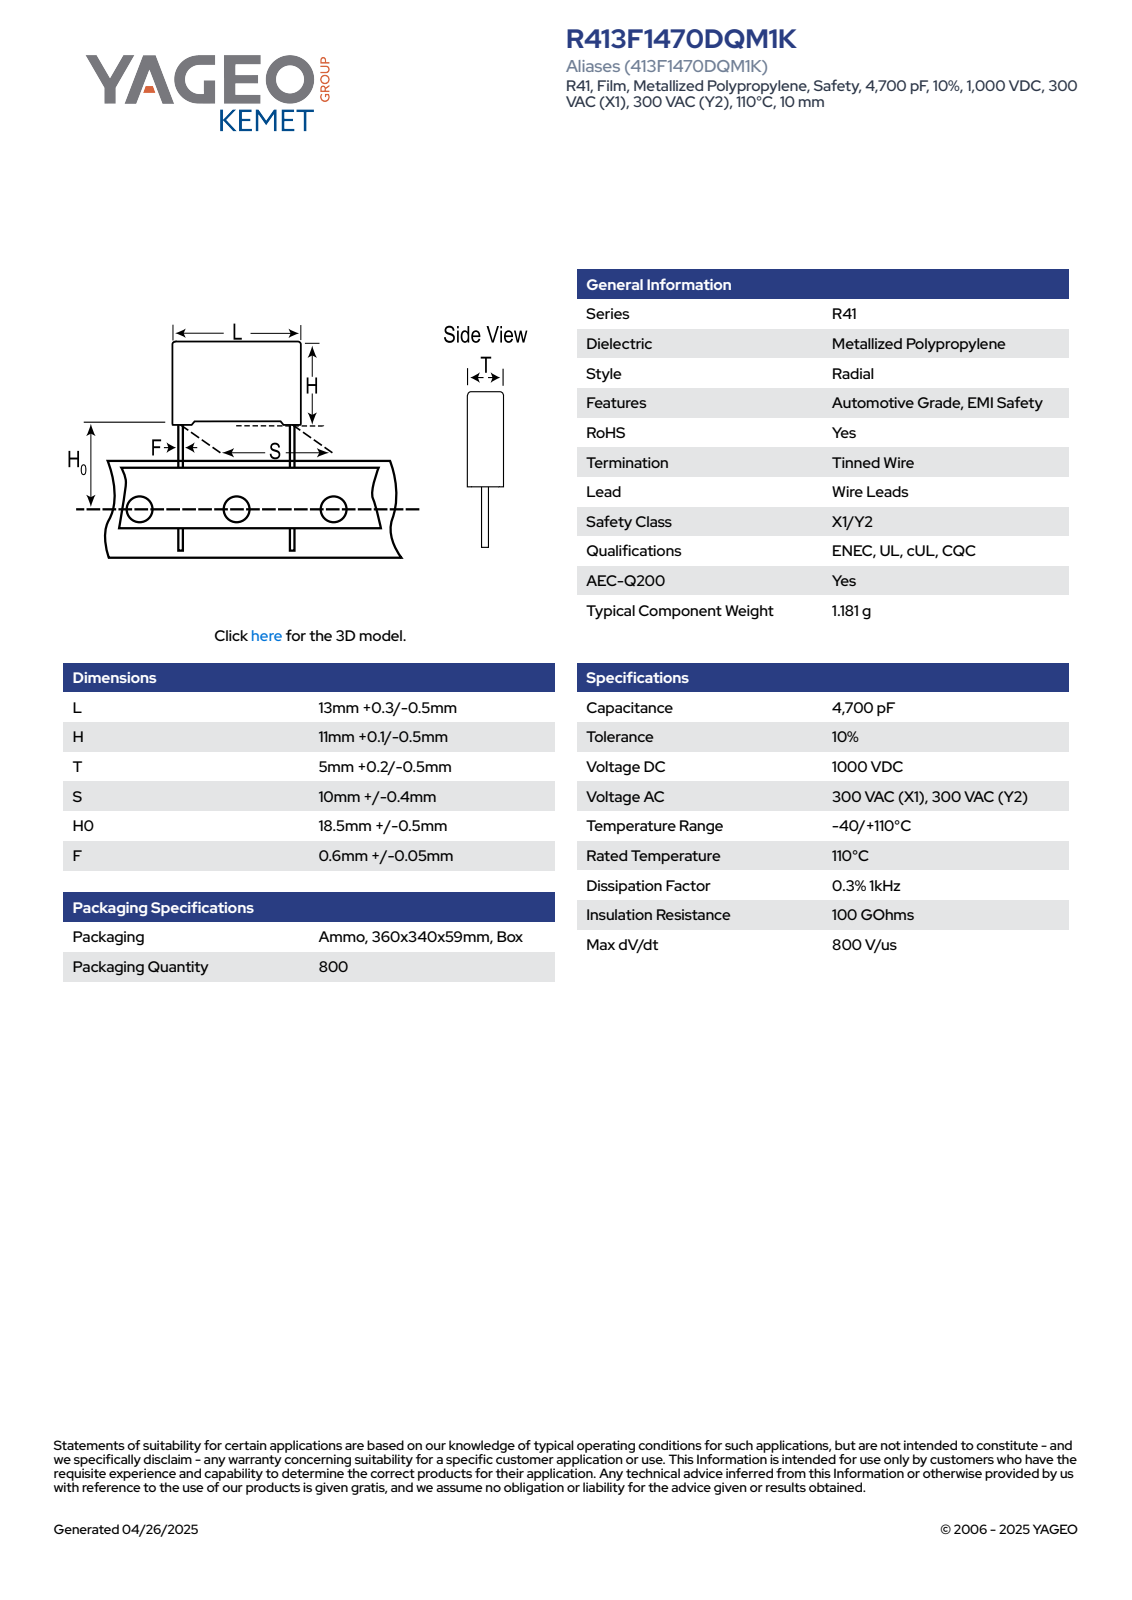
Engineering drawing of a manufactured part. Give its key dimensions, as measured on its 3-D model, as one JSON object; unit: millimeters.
{"part_name": "CFR_RB2_13X11X5_L13.3H11.1T5.2S10H019F0.65", "step_written_by": "SolidWorks 2020 (AUTOMOTIVE_DESIGN)", "units": "millimeters", "bodies": {"solids": 4, "faces": 85, "planar": 77, "cylindrical": 8, "other": 0}, "overall_size": [30.1, 13.3, 5.21], "volume_mm3": 736, "surface_area_mm2": 650, "round_bosses_or_shafts": [[0.65, 2]], "partial_cylinders_radius": [[0.5, 4]], "face_to_face_distances": [5.2, 13.3, 10.35, 0.44, 4.76, 0.75, 11.1, 4.32, 12.86, 0.37]}
